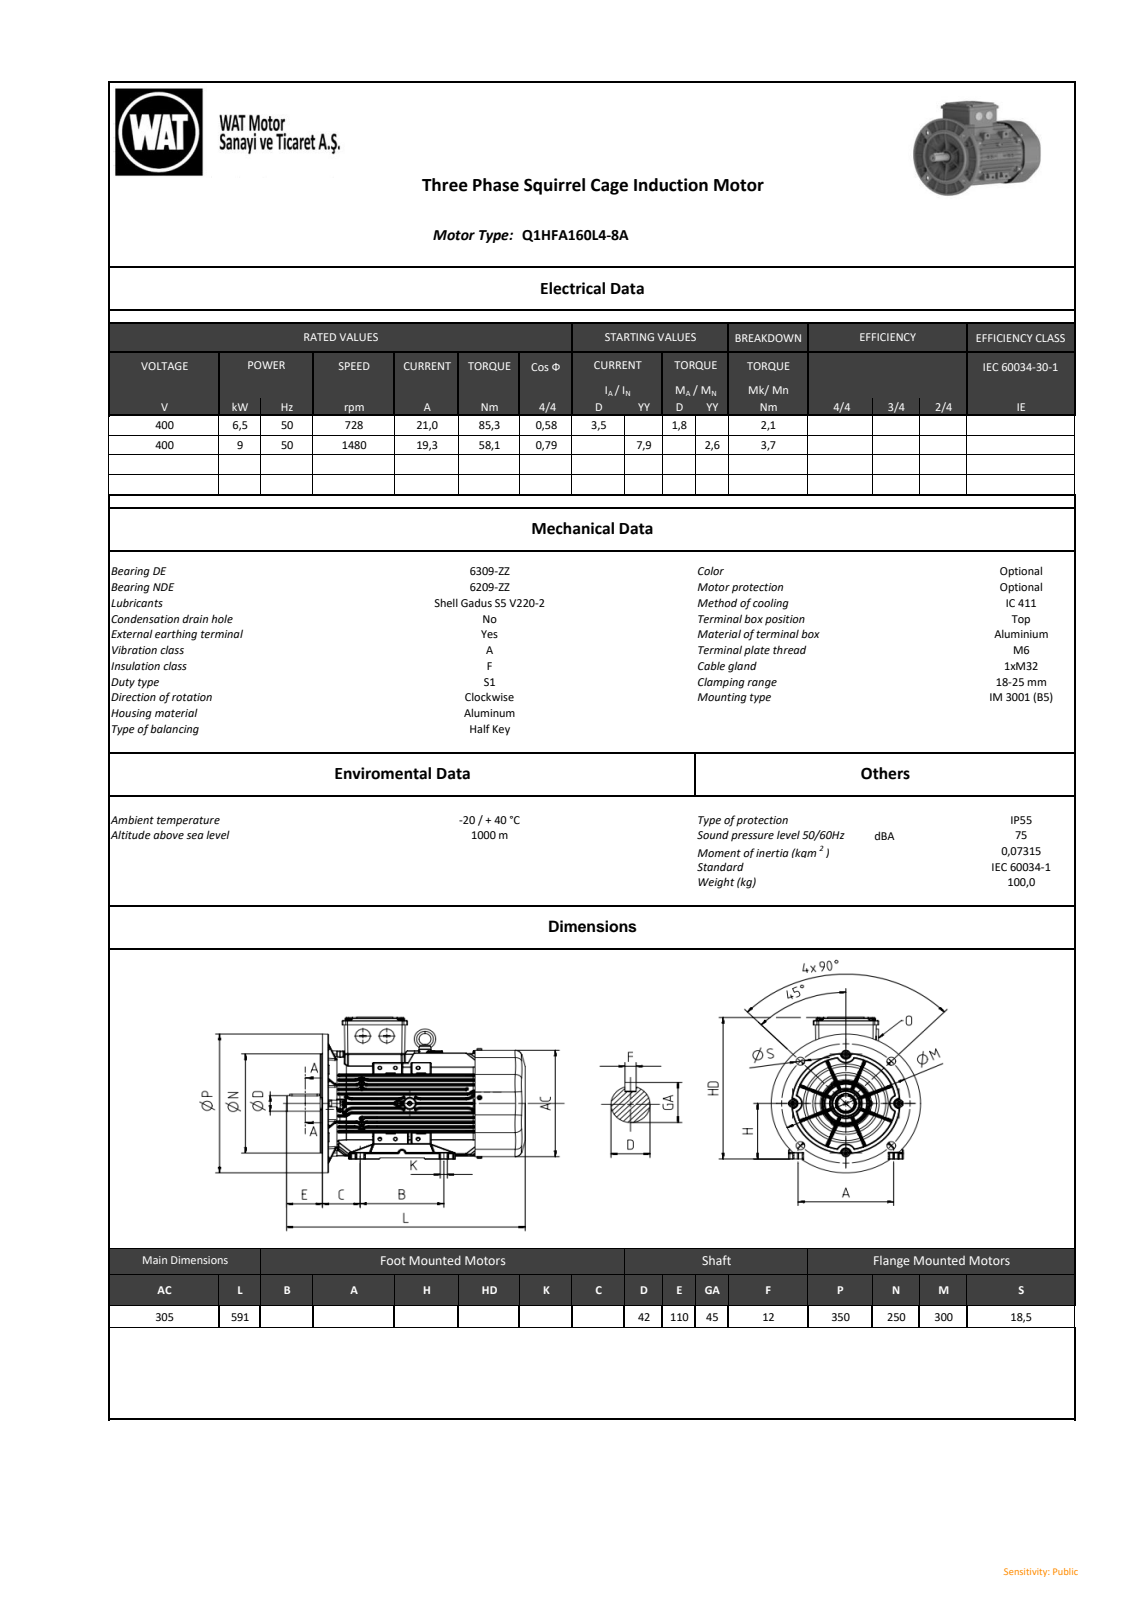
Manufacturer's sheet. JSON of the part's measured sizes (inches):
{"part_name": "QH series_ 160_B5_stp_objects", "step_written_by": "SIEMENS PLM Software NX2206.8101 (AP203_CONFIGURATION_CONTROLLED_3D_DESIGN_OF_MECHANICAL_PARTS_AND_ASSEMBLIES_MIM_LF)", "units": "inches", "bodies": {"solids": 0, "faces": 6510, "planar": 1552, "cylindrical": 2712, "other": 2246}, "overall_size": [23.248, 15.463, 13.78], "round_holes": [[0.65, 4], [0.394, 1], [0.551, 1], [0.669, 1], [2.835, 1], [3.371, 1], [3.701, 1], [4.488, 1], [5.276, 1], [6.063, 1], [6.85, 1], [7.638, 1]], "round_bosses_or_shafts": [[0.315, 4], [1.496, 2], [10.728, 1], [9.843, 1], [7.008, 1], [6.22, 1], [5.433, 1], [4.646, 1]], "partial_cylinders_radius": [[0.02, 670], [0.039, 351], [0.079, 221], [0.157, 81], [0.098, 64], [0.197, 42], [0.236, 34], [0.118, 33]], "face_to_face_distances": [6.614, 5.669, 0.469, 0.379, 0.581, 6.63, 6.251, 0.96, 4.724, 0.467], "hole_center_spacings": [5.61, 7.934, 5.603, 5.604, 5.617, 5.618, 11.22, 5.602]}
